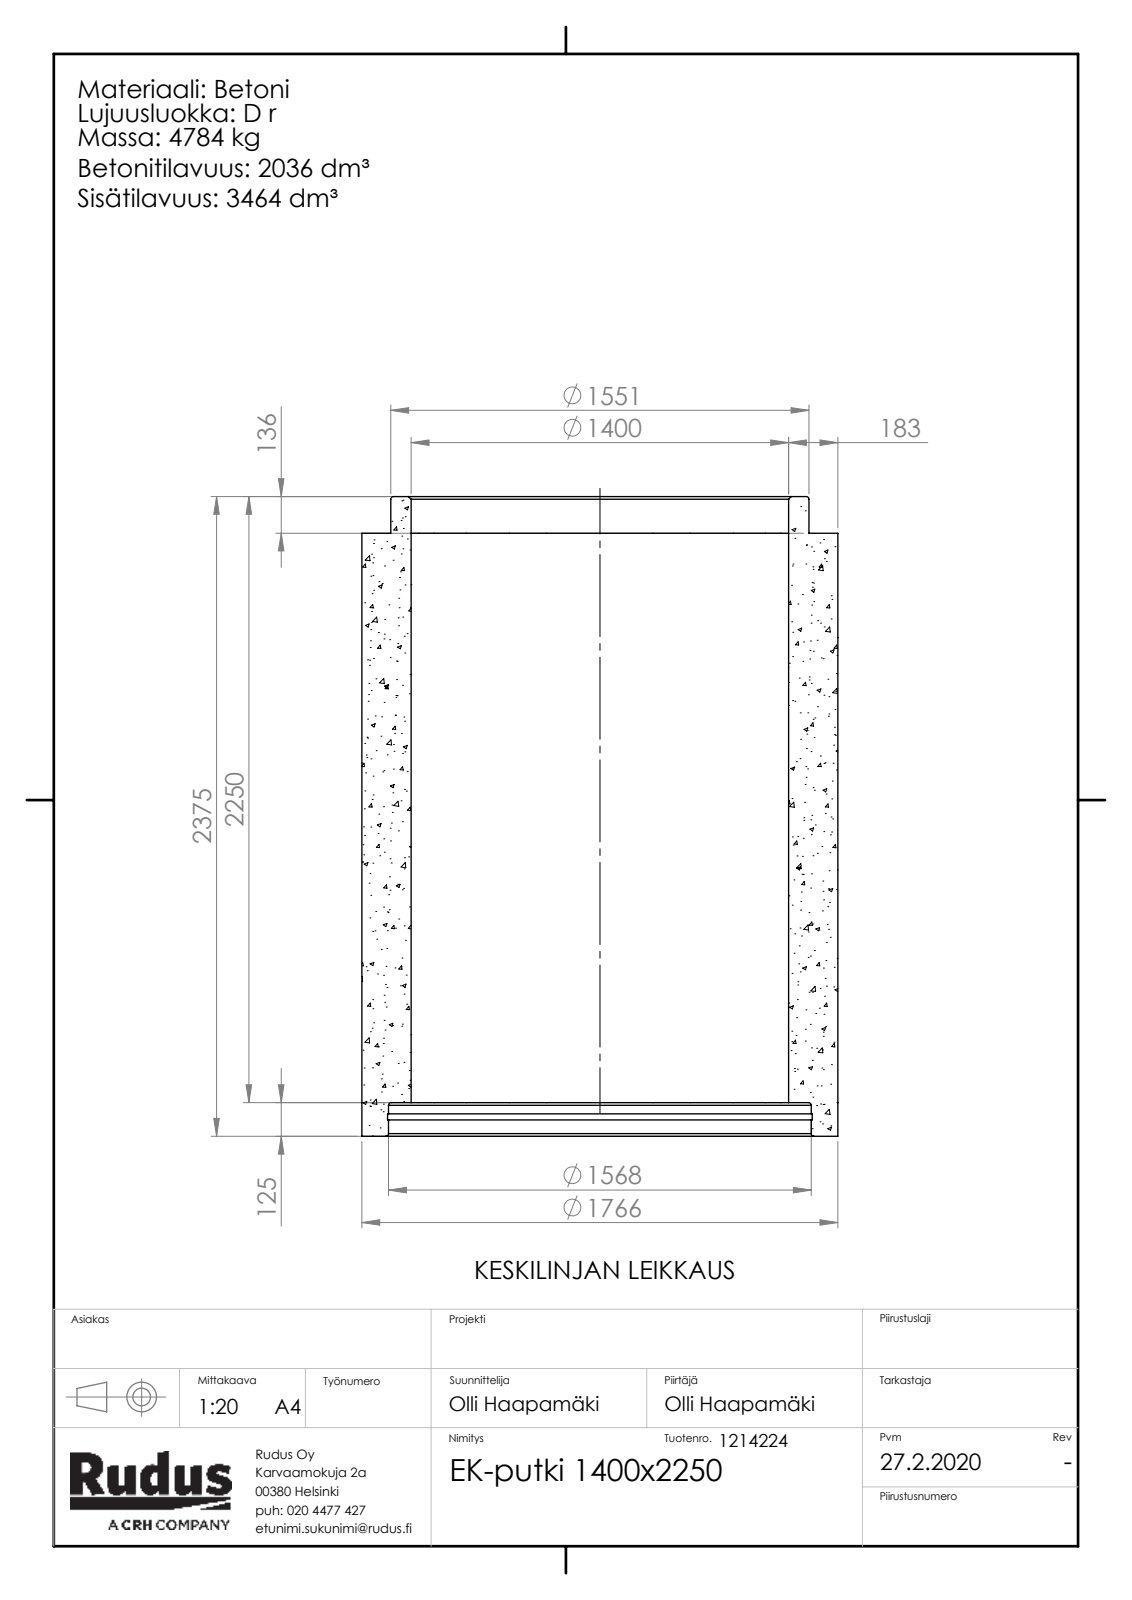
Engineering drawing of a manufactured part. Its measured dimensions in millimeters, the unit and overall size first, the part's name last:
Units: millimetres
Overall size (bounding box): 2375 × 1766 × 1766
Round holes (diameter × count): ⌀1400 ×1, ⌀1568 ×1, ⌀1576 ×1
Round bosses / shafts (diameter × count): ⌀1766 ×1, ⌀1551.4 ×1
Main face-to-face distances: 2239, 125, 2114, 2375, 2250, 136, 61, 64, 2178, 2314
Volume: 2 036 000 000 mm³ · Surface area: 25 370 000 mm²
Bodies: 1 solid, 107 faces (7 planar, 12 cylindrical, 88 other)
Part name (STEP PRODUCT): EK-osa-putkirunko; Rudus 1214224 EK-putki 1400x2250
STEP written by: SolidWorks 2019 (CONFIG_CONTROL_DESIGN)
